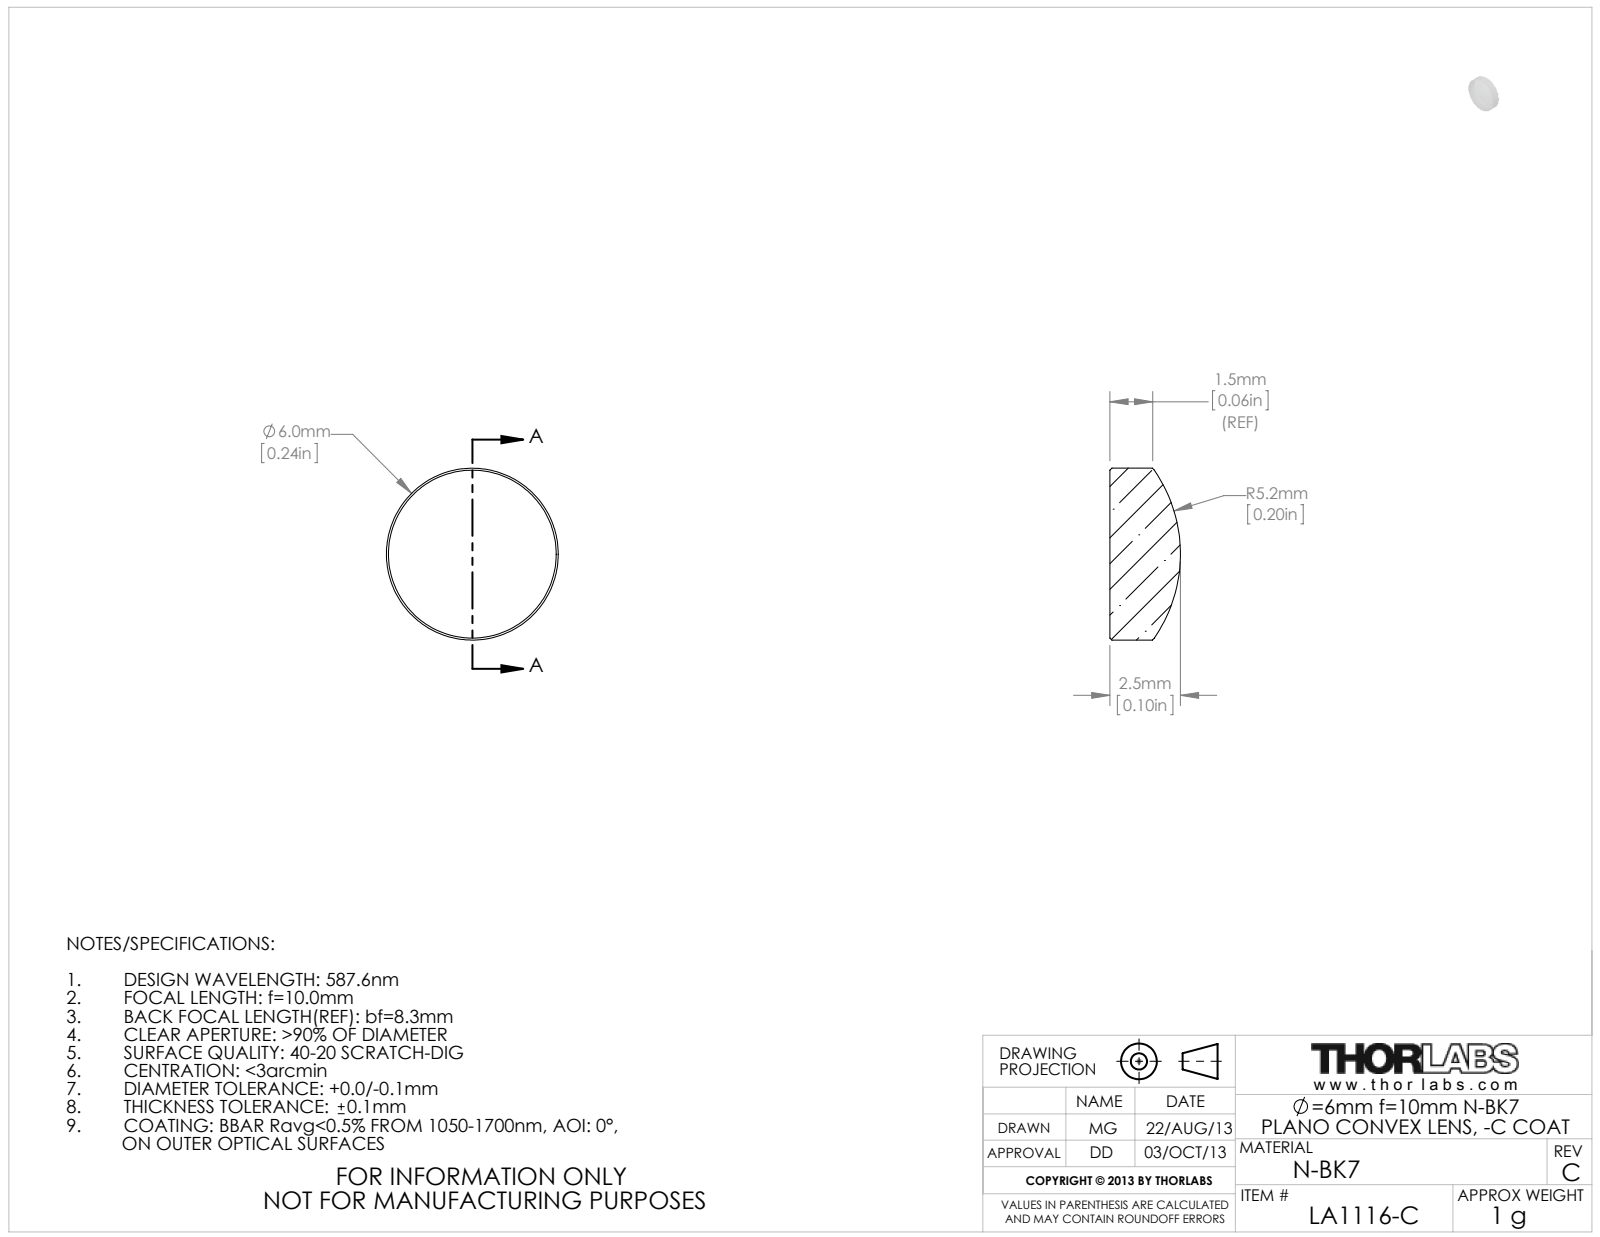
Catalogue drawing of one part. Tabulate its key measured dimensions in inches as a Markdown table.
| quantity | value |
| --- | --- |
| part name | 4562-E0W |
| STEP written by | SolidWorks 2009 (AUTOMOTIVE_DESIGN) |
| units | inches |
| bodies | 1 solid, 5 faces (1 planar, 2 cylindrical, 2 other) |
| overall size | 0.236 × 0.236 × 0.097 |
| volume | 0.003 in³ |
| surface area | 0.14 in² |
| round bosses / shafts (diameter × count) | 0.236 × 1 |
